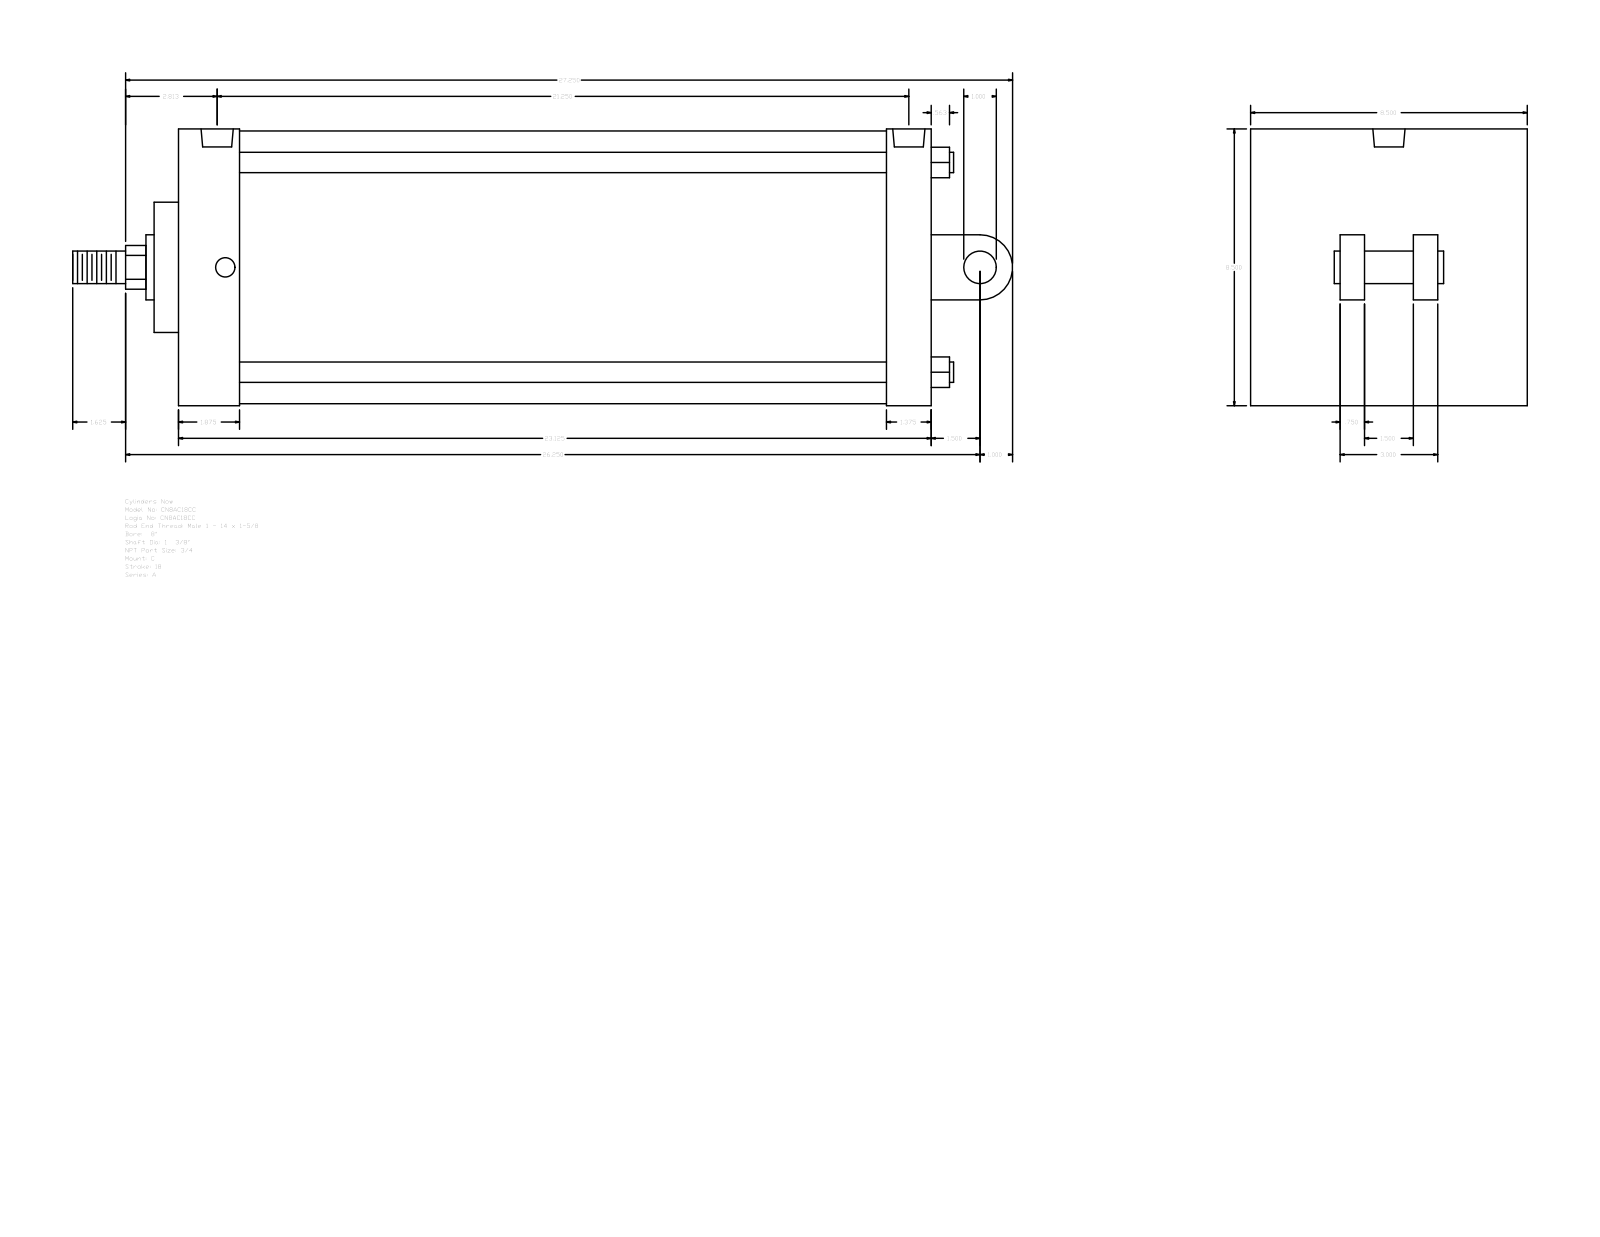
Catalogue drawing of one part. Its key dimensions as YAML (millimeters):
part_name: "A_C__0800_1.375"
step_written_by: "GSSL Pune (CONFIG_CONTROL_DESIGN)"
units: millimeters
bodies: {solids: 0, faces: 104, planar: 75, cylindrical: 29, other: 0}
overall_size: [733.42, 215.9, 215.9]
round_holes:
  - {diameter: 15.08, count: 4}
  - {diameter: 25.12, count: 2}
round_bosses_or_shafts:
  - {diameter: 15.88, count: 4}
  - {diameter: 25.4, count: 2}
  - {diameter: 212.72, count: 1}
  - {diameter: 50.8, count: 1}
  - {diameter: 34.92, count: 1}
partial_cylinders:
  - {radius: 17.06, count: 1}
  - {radius: 25.4, count: 1}
face_to_face_distances: [587.38, 215.9, 57.15, 47.63, 539.75, 552.46, 504.83, 34.92, 88.9, 69.85]
hole_center_spacings: [6.35, 527.05, 533.4, 539.75]
